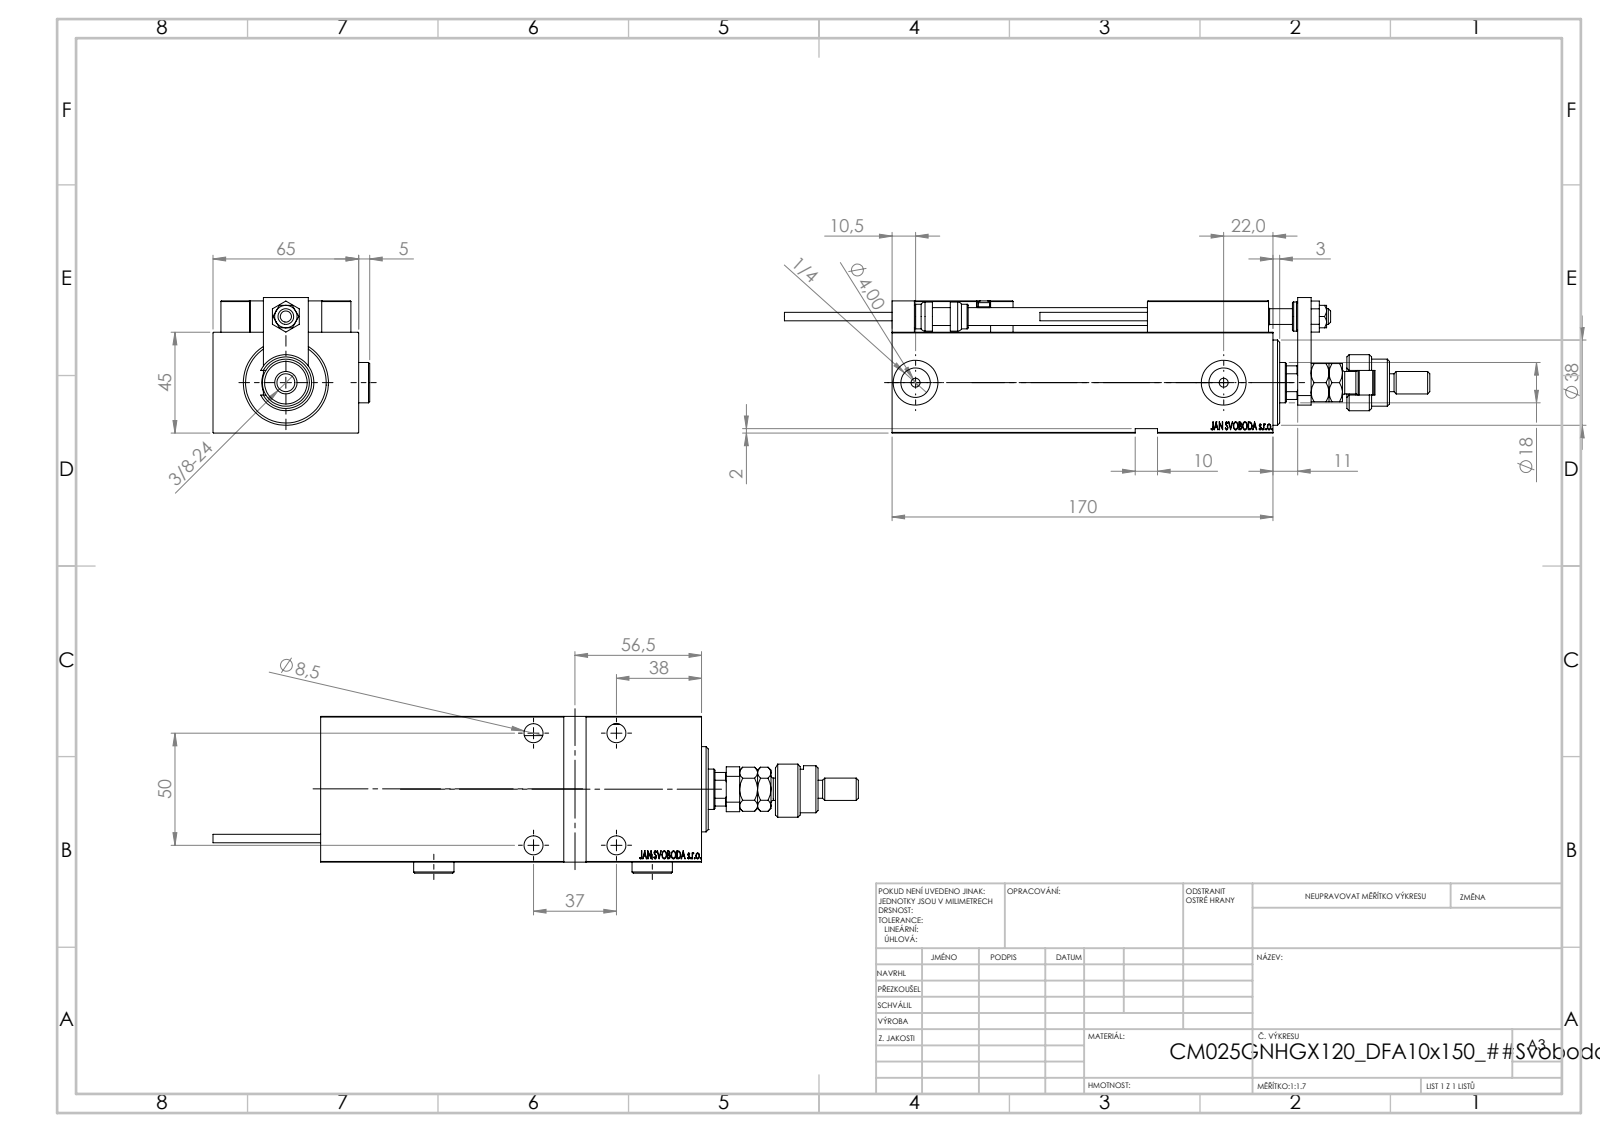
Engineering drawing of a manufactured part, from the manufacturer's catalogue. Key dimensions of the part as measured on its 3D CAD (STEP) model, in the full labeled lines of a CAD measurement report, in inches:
Part name (STEP PRODUCT): X_Y_DFA; ALLEN BOLT D5; V450CM_G_VCP; NUT_D10 (+7 more)
STEP written by: SolidWorks 2019 (CONFIG_CONTROL_DESIGN)
Units: inches
Bodies: 28 solids, 1419 faces (629 planar, 201 cylindrical, 589 other)
Overall size (bounding box): 11.339 × 2.752 × 2.382
Volume: 31.6 in³ · Surface area: 173 in²
Round holes (diameter × count): ⌀0.157 ×6, ⌀0.315 ×5, ⌀0.335 ×5, ⌀0.126 ×4, ⌀0.531 ×4, ⌀0.197 ×2, ⌀0.518 ×2, ⌀0.787 ×2, ⌀0.276 ×1, ⌀0.571 ×1, ⌀0.709 ×1, ⌀0.846 ×1
Round bosses / shafts (diameter × count): ⌀0.709 ×2, ⌀0.197 ×2, ⌀0.15 ×2, ⌀1.496 ×1, ⌀0.984 ×1, ⌀0.827 ×1, ⌀0.63 ×1, ⌀0.512 ×1
Partial cylindrical surfaces — rounded edges, fillets, slot ends (radius × count): R0.012 ×30, R0.118 ×2, R0.217 ×1, R0.335 ×1, R0.344 ×1
Main face-to-face distances: 1.772, 2.559, 0.551, 0.236, 2.323, 6.693, 0.748, 0.197, 7.126, 0.512
Hole centre spacings: 0.448, 0.787, 1.165, 1.169, 1.356, 1.42, 1.457, 1.661
